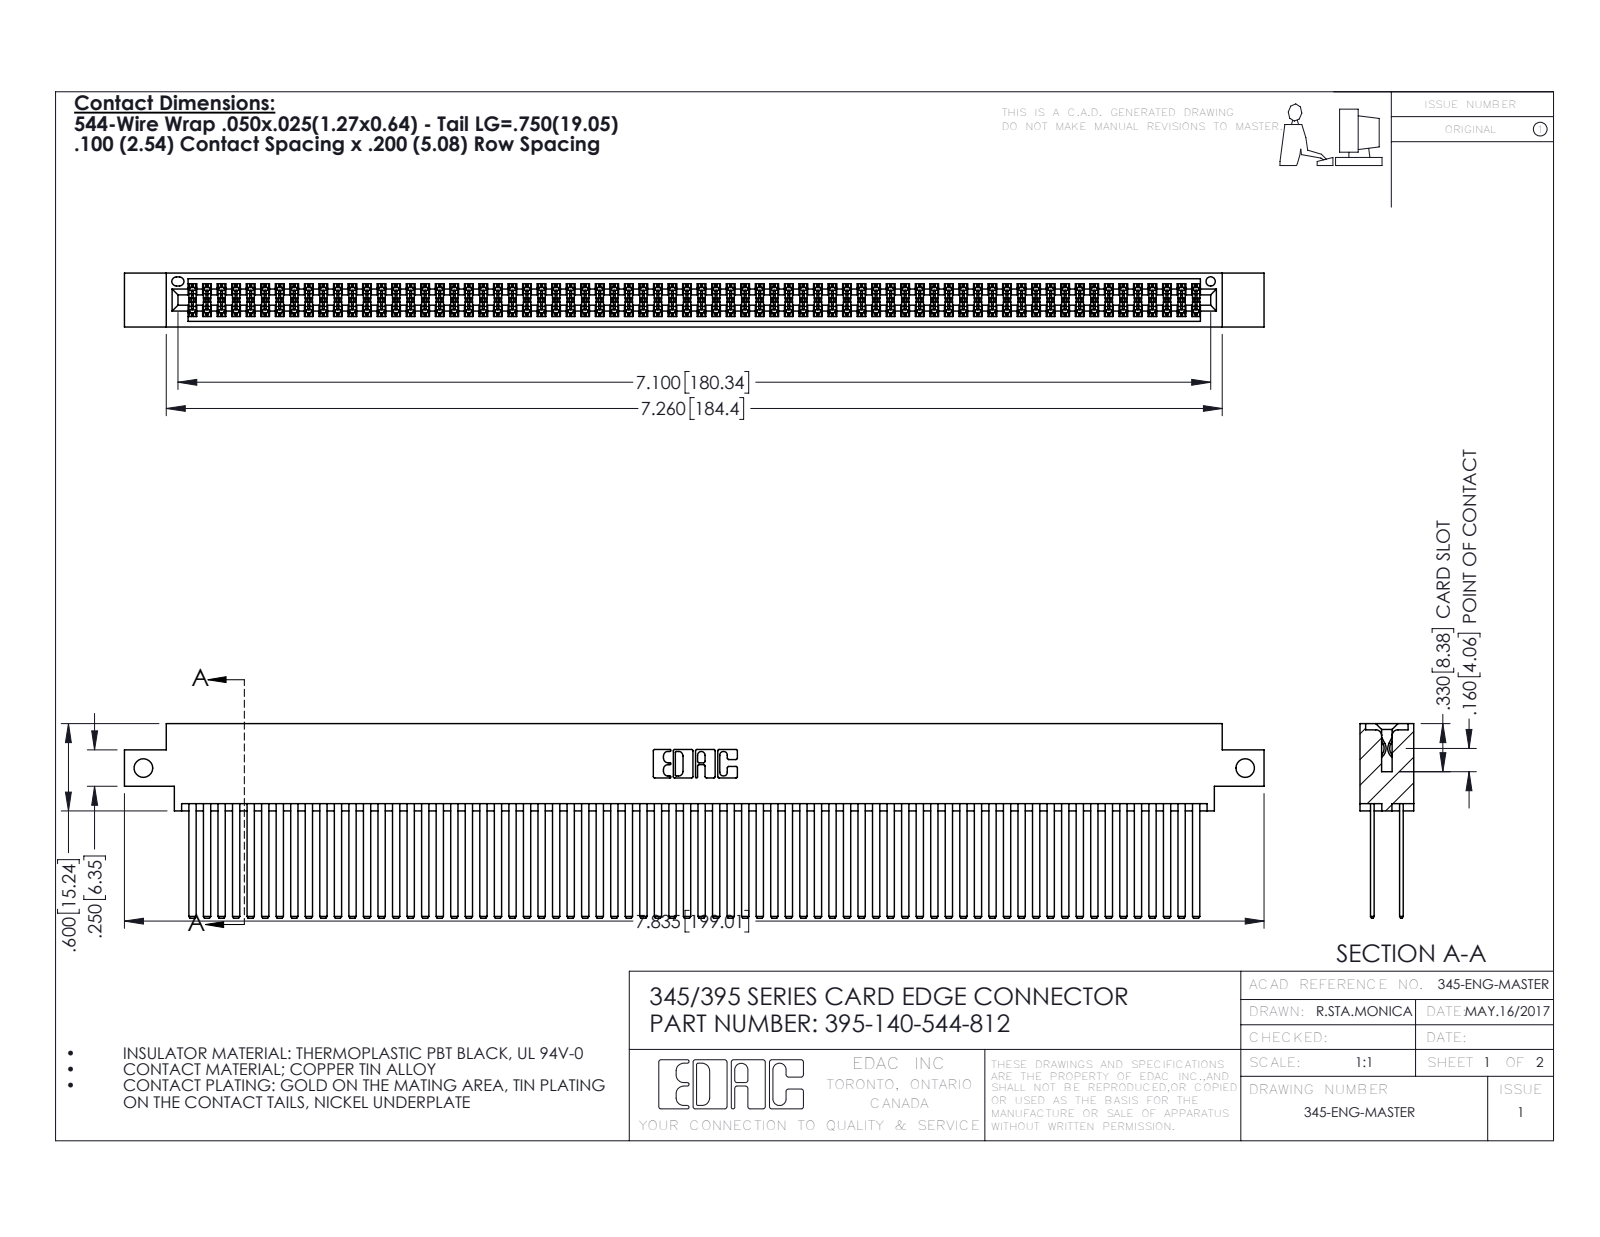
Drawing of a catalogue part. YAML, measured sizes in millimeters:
part_name: "345 Part_0.170 Offset - Side Mount; 345-292-001_345-293-144; 395-140-544-812"
step_written_by: "SolidWorks 2016 (CONFIG_CONTROL_DESIGN)"
units: millimeters
bodies: {solids: 141, faces: 6290, planar: 4144, cylindrical: 2146, other: 0}
overall_size: [199, 34, 9.4]
volume: 21350
surface_area: 37860
round_holes:
  - {diameter: 3.3, count: 2}
  - {diameter: 1.6, count: 1}
partial_cylinders:
  - {radius: 0.2, count: 210}
  - {radius: 0.3, count: 22}
  - {radius: 0.2, count: 6}
  - {radius: 0.8, count: 6}
  - {radius: 0.7, count: 3}
  - {radius: 0.4, count: 2}
  - {radius: 0.5, count: 2}
  - {radius: 0.6, count: 2}
face_to_face_distances: [5.1, 0.6, 7.6, 1.8, 2.5, 6.9, 5.7, 4.4, 9.4, 3.8]
hole_center_spacings: [192.4]
